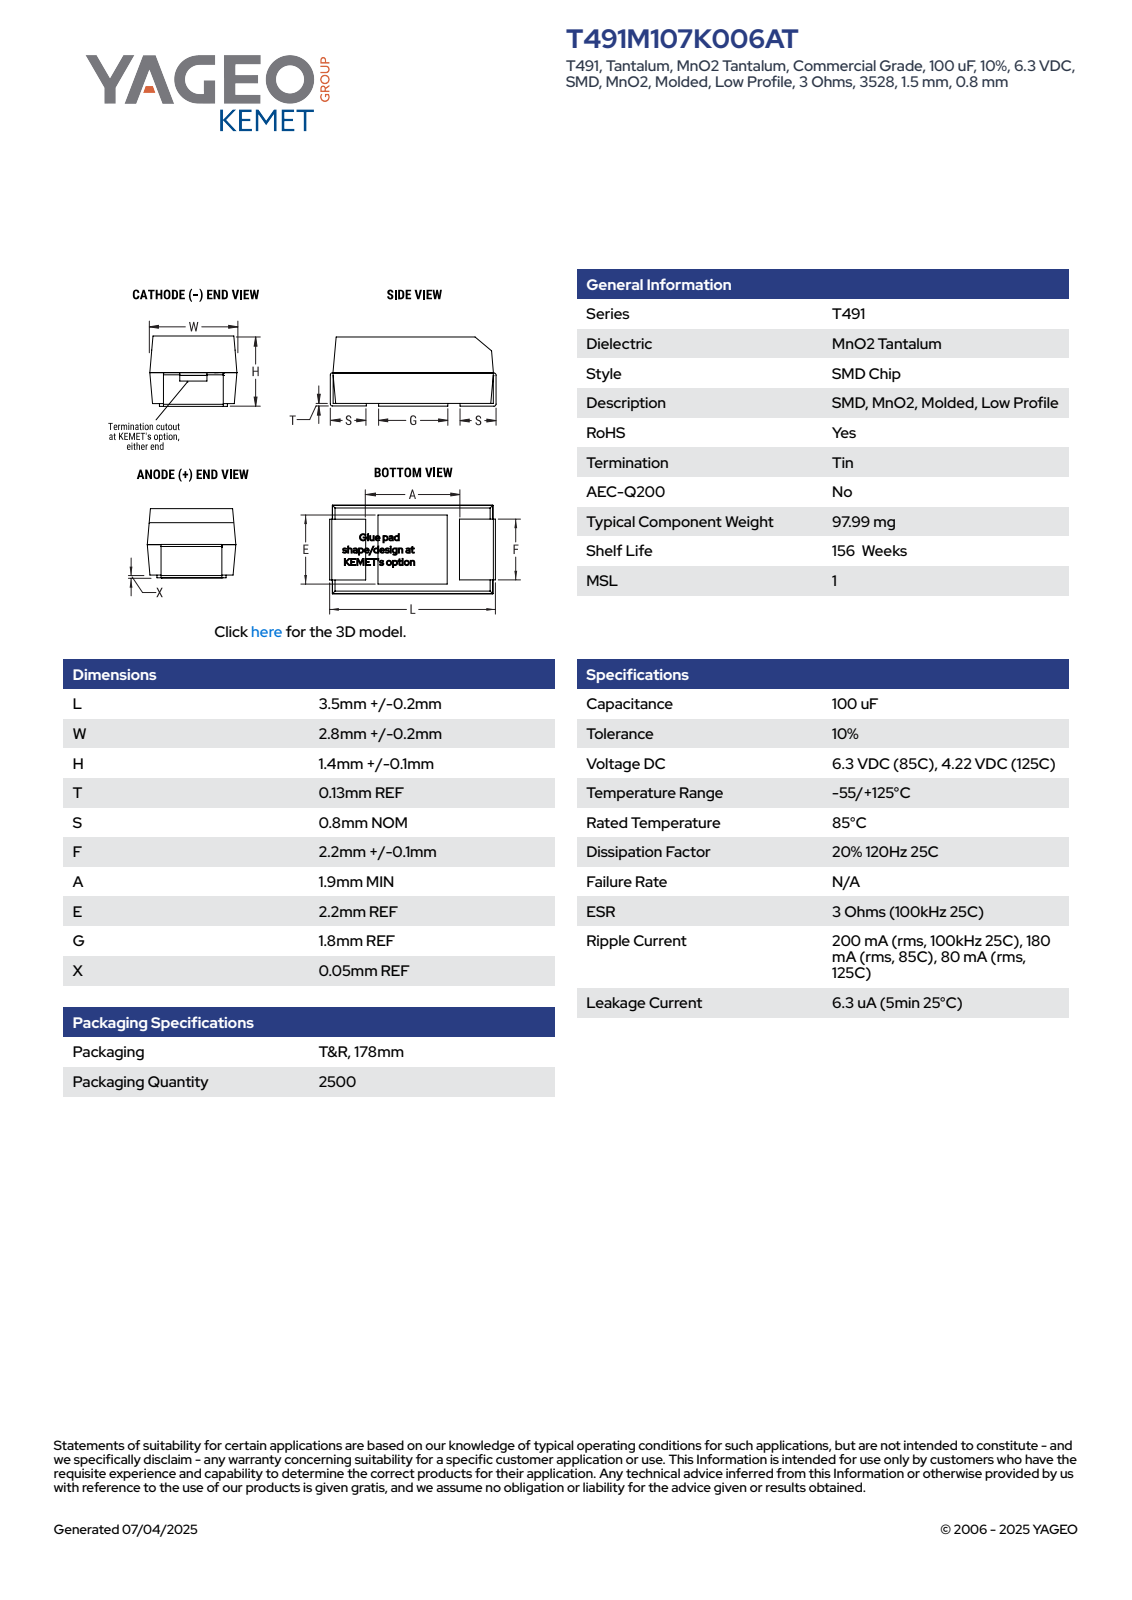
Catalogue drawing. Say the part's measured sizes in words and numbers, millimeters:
The part is named "CTSM_TCM2NBKRP_3528_L3.7W3H1.5T0.13S0.8F2.3A1.9E2.2G1.8X0.05". Its 3-D file was written by "SolidWorks 2020 (AUTOMOTIVE_DESIGN)". It is 4 solids with 94 faces: 90 planar, 4 cylindrical and 0 other. Overall it measures 3.7 by 3 by 1.5 millimeters. Its volume is 14 cubic millimeters and its surface area 43 square millimeters. Partial cylindrical surfaces (rounded edges, fillets, slot ends): 4 of radius 0.1. The main face-to-face distances are 1.5, 2.92, 2.93, 3.57, 3.7, 1.45, 3.44, 1.37, 0.75, 2.3.
